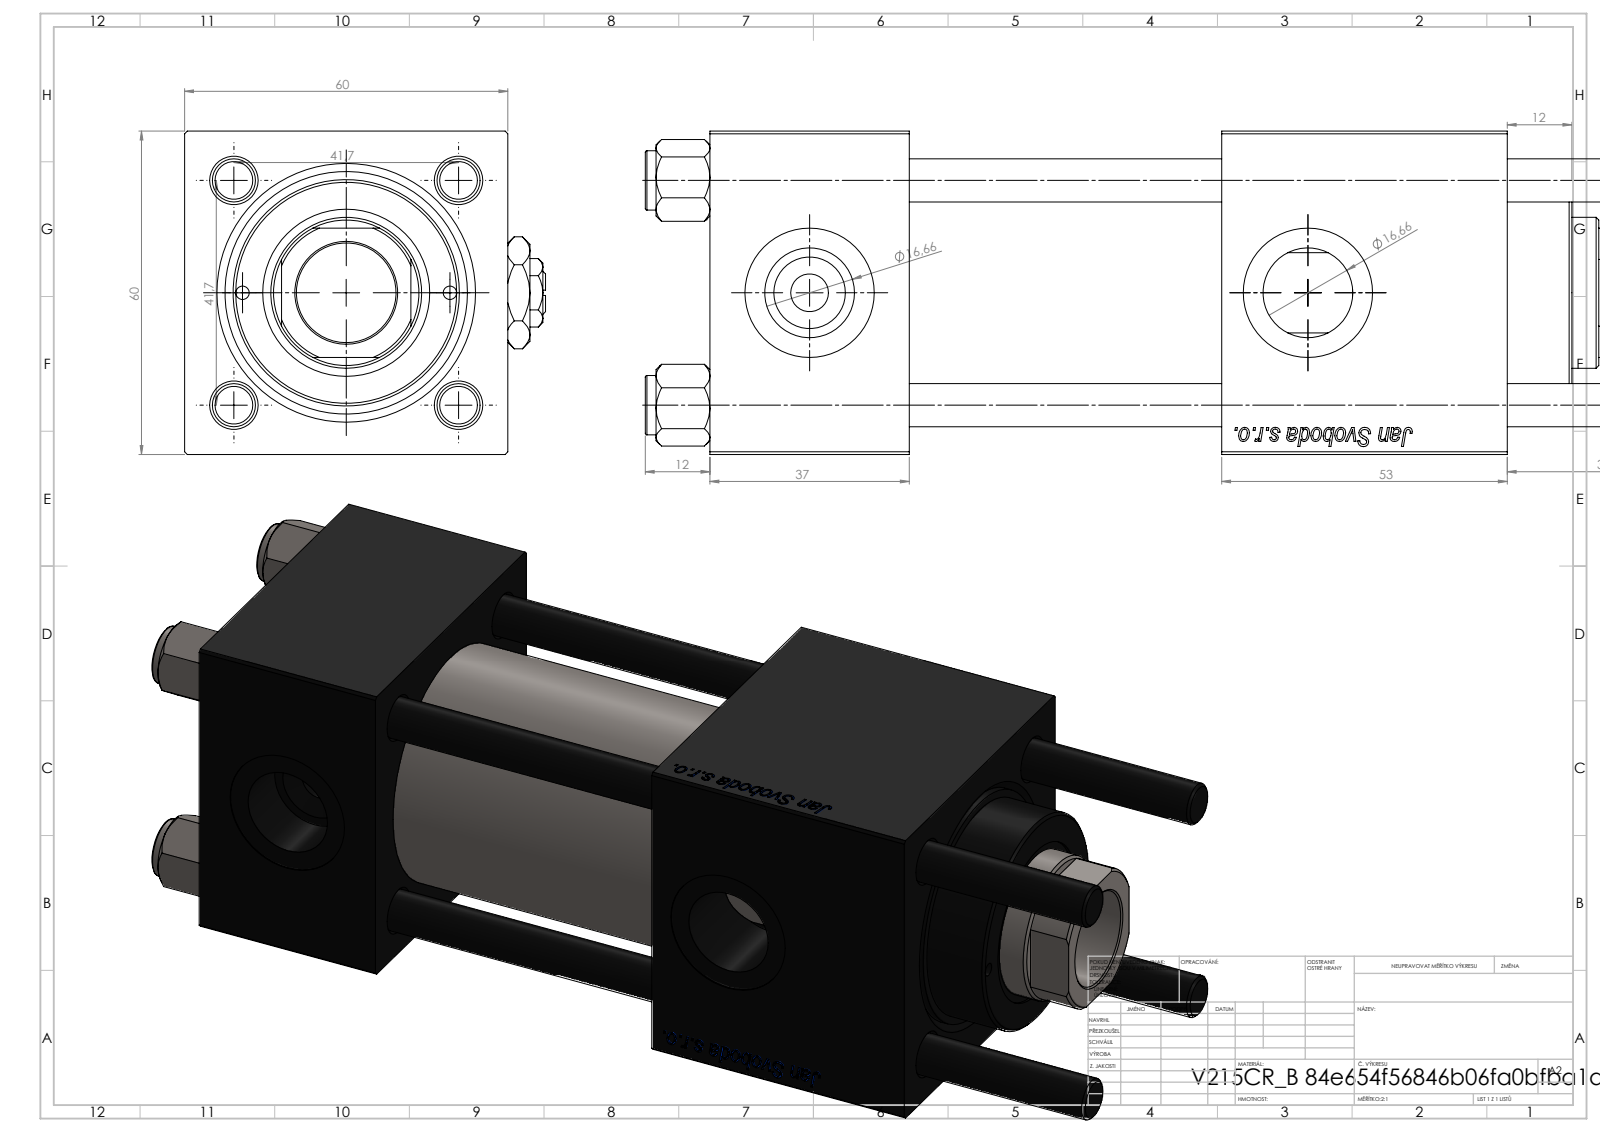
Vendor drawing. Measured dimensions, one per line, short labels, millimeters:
name: Zatka_pro_OIL_PORT; V215CR_VCP_B; V215CR_B_TYCINKA; V215_VC_A (+2 more)
written by: SolidWorks 2019 (CONFIG_CONTROL_DESIGN)
unit: mm
bodies: 12 solids, 1213 faces (459 planar, 86 cylindrical, 668 other)
size: 195 × 67 × 60
volume: 433 517 mm³; area: 121 390 mm²
holes: 4× ⌀8, 2× ⌀2.5, 2× ⌀7, 2× ⌀16.66, 2× ⌀24, 1× ⌀18.5, 1× ⌀28, 1× ⌀31, 1× ⌀40, 1× ⌀45
bosses: 4× ⌀11, 1× ⌀46, 1× ⌀42
rounds: 1× R13.5
face distances: 60, 37, 58, 95, 53, 119.3, 82.3, 24.3, 148, 111
hole spacings: 20.91, 29.49, 41.7, 45.2, 19.25, 58.97, 38.5, 92.5
